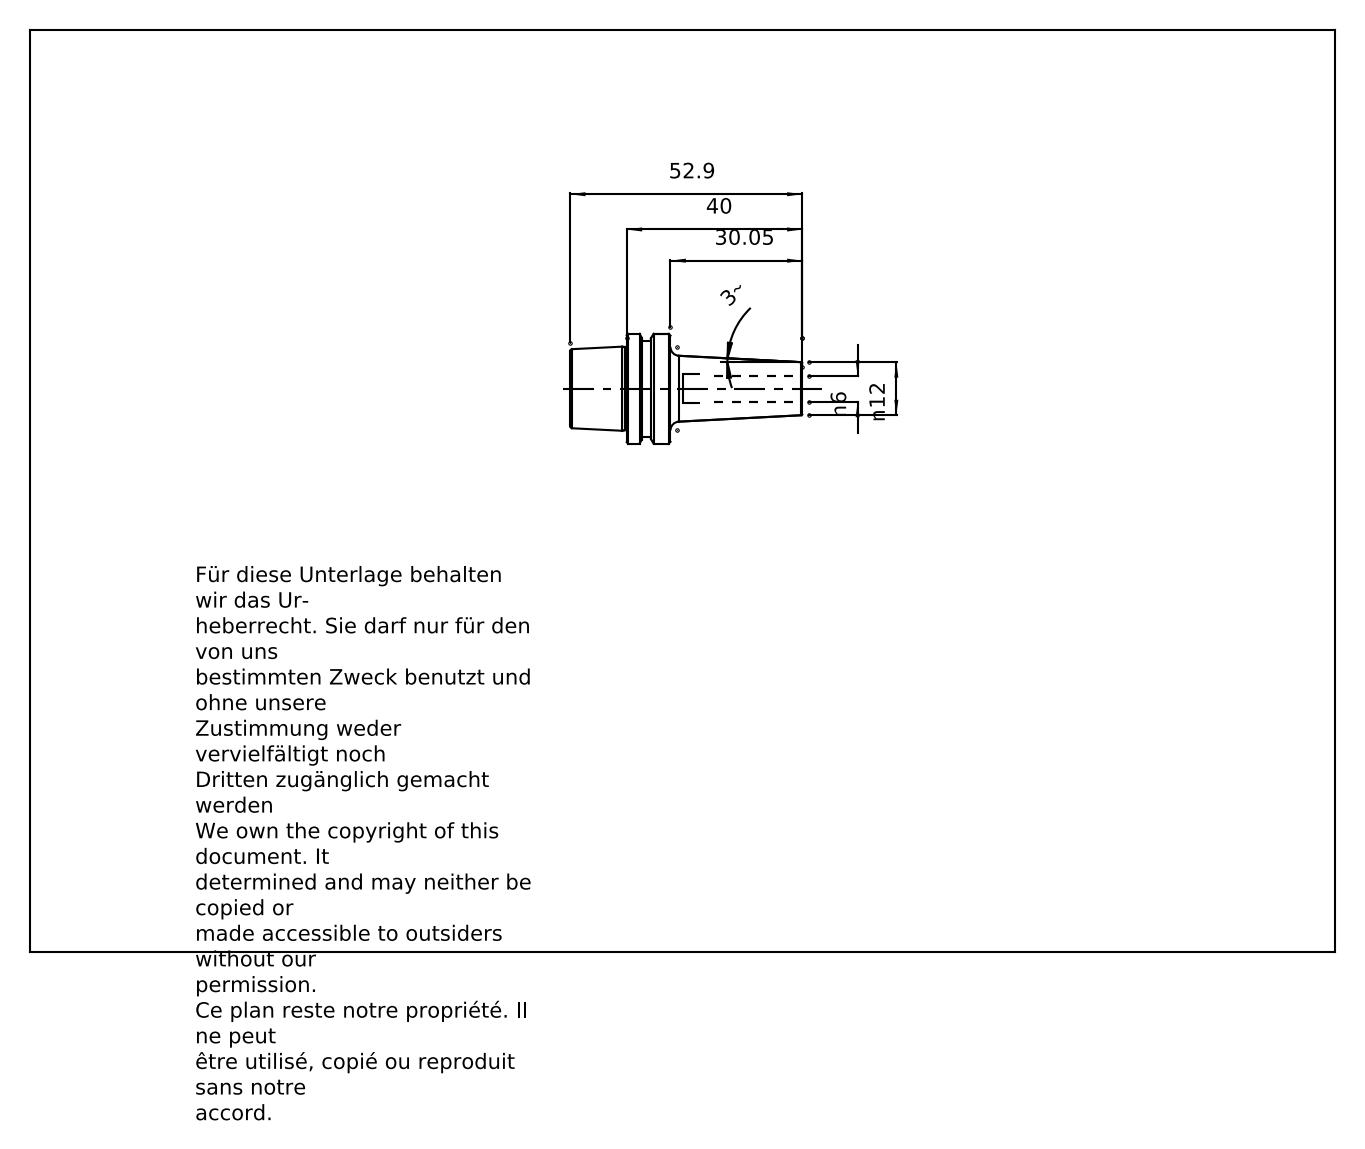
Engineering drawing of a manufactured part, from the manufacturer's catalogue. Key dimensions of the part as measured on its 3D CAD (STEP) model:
Part name (STEP PRODUCT): E25-185-06
STEP written by: PRO/ENGINEER BY PARAMETRIC TECHNOLOGY CORPORATION, 2010430 (CONFIG_CONTROL_DESIGN)
Units: millimetres
Bodies: 1 solid, 60 faces (8 planar, 16 cylindrical, 36 other)
Overall size (bounding box): 52.9 × 25 × 25
Volume: 8 430 mm³ · Surface area: 5 224 mm²
Round holes (diameter × count): ⌀6 ×1, ⌀14.04 ×1, ⌀16.45 ×1
Round bosses / shafts (diameter × count): ⌀25 ×1, ⌀21.95 ×1, ⌀18.96 ×1
Main face-to-face distances: 4, 5.95, 9.95, 40, 34.05, 30.05, 12.9, 18.85, 22.85, 52.9
